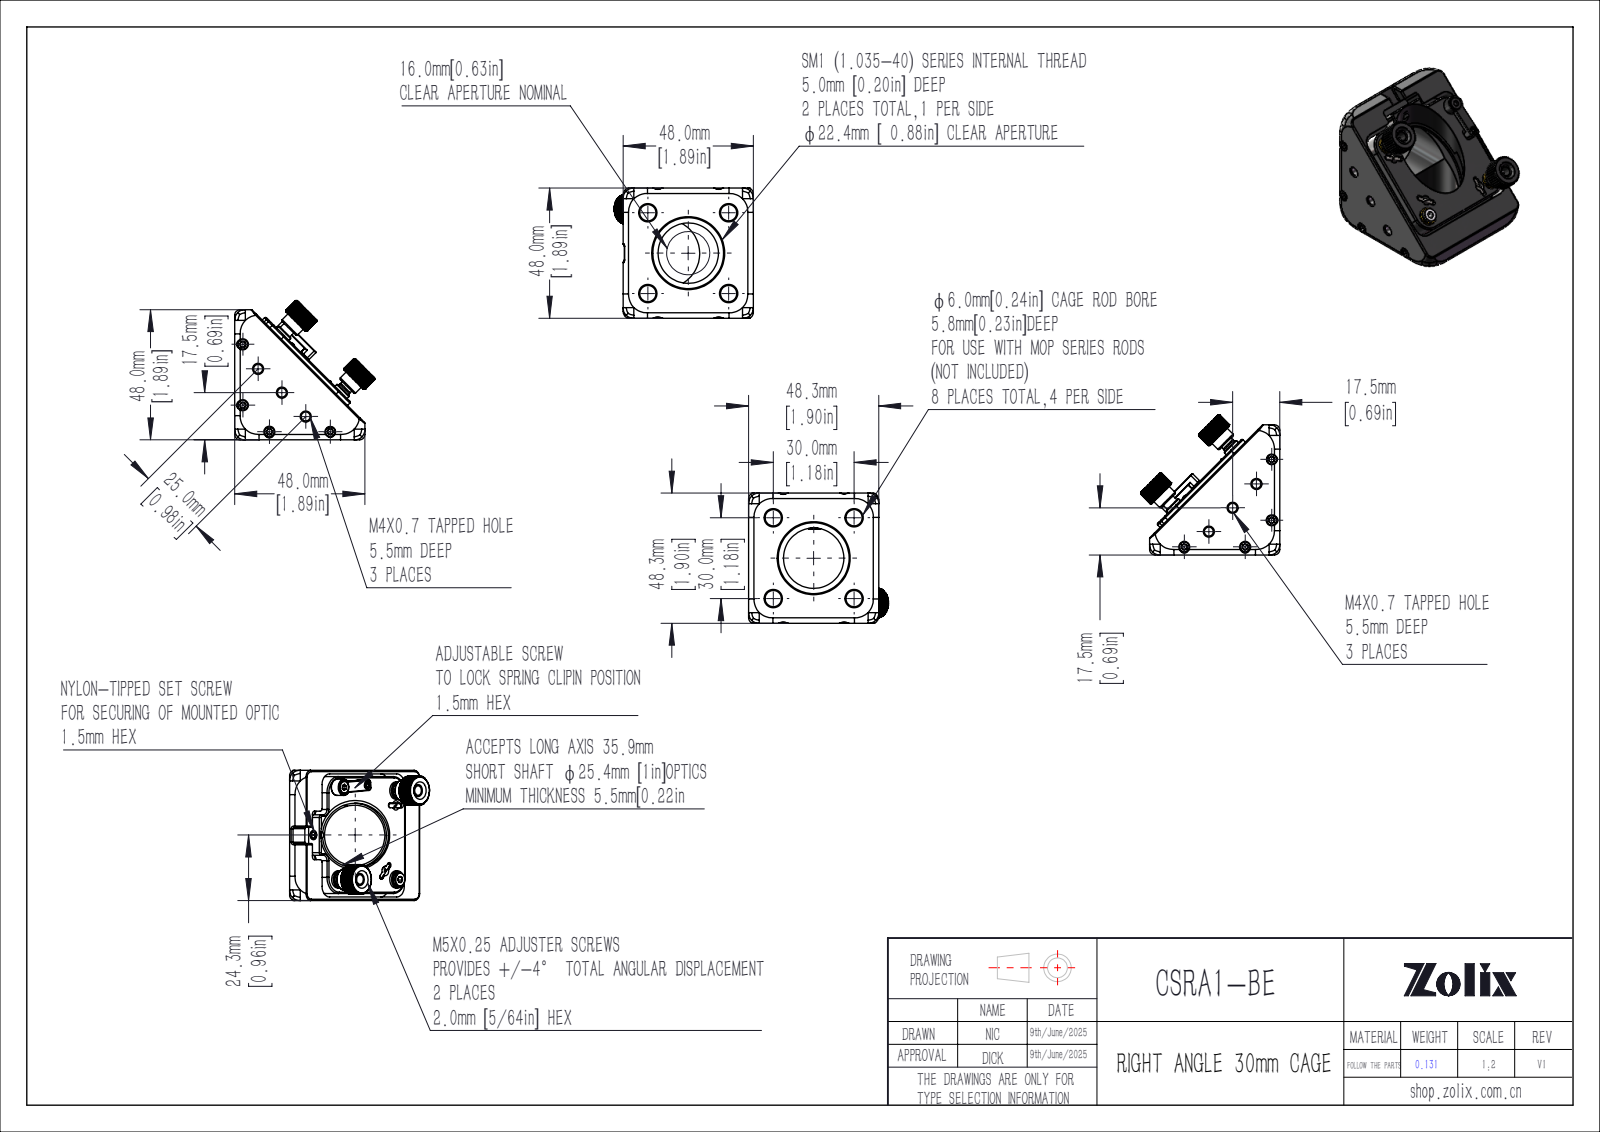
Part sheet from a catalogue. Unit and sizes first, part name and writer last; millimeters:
Units: millimetres
Overall size (bounding box): 51.94 × 51.65 × 48.3
Round holes (diameter × count): ⌀6 ×9, ⌀3.3 ×7, ⌀3.5 ×5, ⌀5 ×4, ⌀1.6 ×3, ⌀1.95 ×3, ⌀2.05 ×3, ⌀2.4 ×3, ⌀2.5 ×3, ⌀6.4 ×3, ⌀7.3 ×3, ⌀4.3 ×2
Round bosses / shafts (diameter × count): ⌀4 ×5, ⌀6 ×4, ⌀2.5 ×4, ⌀7.1 ×3, ⌀1.6 ×3, ⌀8 ×2, ⌀6.4 ×2, ⌀4.5 ×1
Partial cylindrical surfaces — rounded edges, fillets, slot ends (radius × count): R0.5 ×42, R1 ×16, R2 ×13, R0.2 ×9, R0.9 ×6, R0.3 ×4, R4 ×4, R6 ×4
Main face-to-face distances: 48.3, 1, 4, 3, 10.1, 6.1, 7.1, 1.3, 4.4, 1.7
Hole centre spacings: 21.21, 30, 5.5, 42.43, 25.2, 30.32, 40.14, 41.4
Volume: 44 958 mm³ · Surface area: 26 326 mm²
Bodies: 35 solids, 1662 faces (768 planar, 408 cylindrical, 486 other)
Part name (STEP PRODUCT): CSRA1-BE
STEP written by: SolidWorks 2020 (CONFIG_CONTROL_DESIGN)
